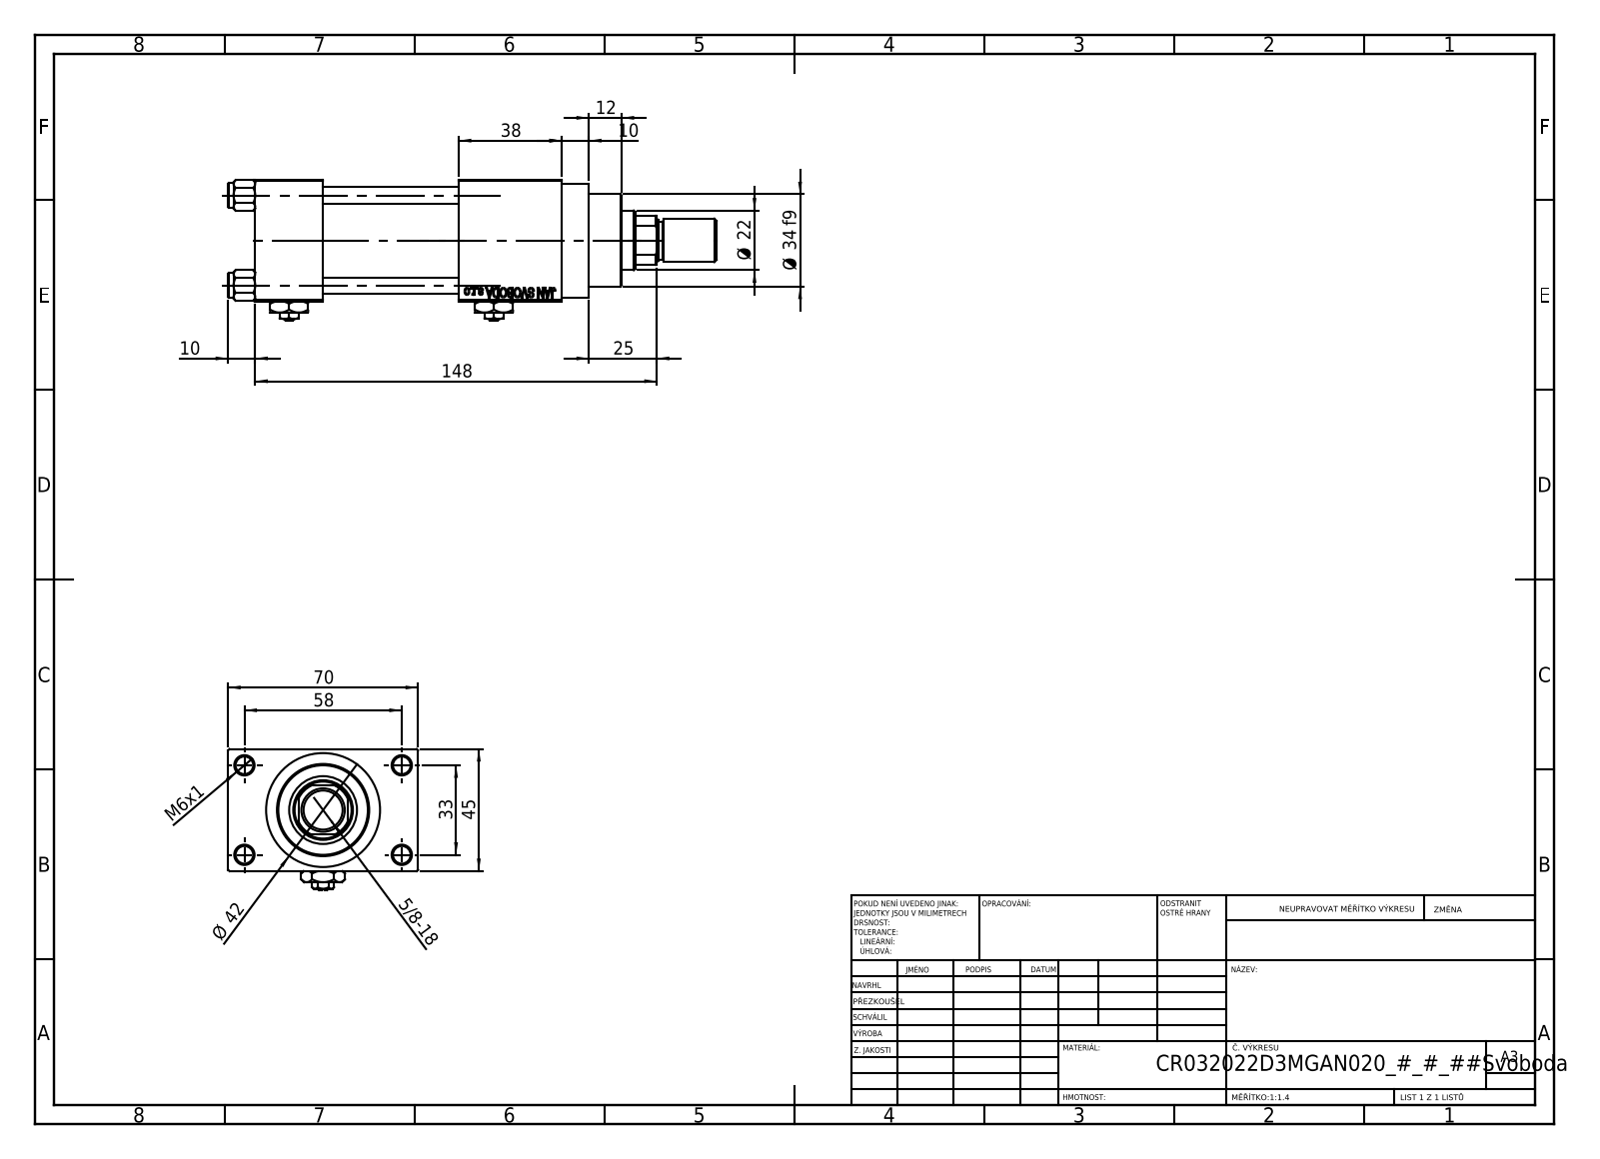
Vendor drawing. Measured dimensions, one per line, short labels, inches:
name: V215_VC_A; ROD_END_AH; V215CR_D_TYCINKA; NUT_M5_D (+3 more)
written by: SolidWorks 2019 (CONFIG_CONTROL_DESIGN)
unit: in
bodies: 14 solids, 1216 faces (546 planar, 104 cylindrical, 566 other)
size: 7.087 × 2.756 × 2.047
volume: 15.11 in³; area: 128.2 in²
holes: 4× ⌀0.236, 4× ⌀0.256, 2× ⌀0.276, 2× ⌀0.518, 2× ⌀0.787, 1× ⌀0.413, 1× ⌀0.866, 1× ⌀0.945, 1× ⌀0.984, 1× ⌀1.26, 1× ⌀1.299
bosses: 4× ⌀0.354, 1× ⌀1.654, 1× ⌀1.496, 1× ⌀1.339, 1× ⌀0.63, 1× ⌀0.551
rounds: 1× R0.413
face distances: 1.772, 0.984, 0.492, 2.264, 1.969, 2.953, 3.465, 2.756, 1.496, 4.449
hole spacings: 0.488, 0.924, 1.307, 1.314, 1.392, 1.795, 2.219, 1.299
